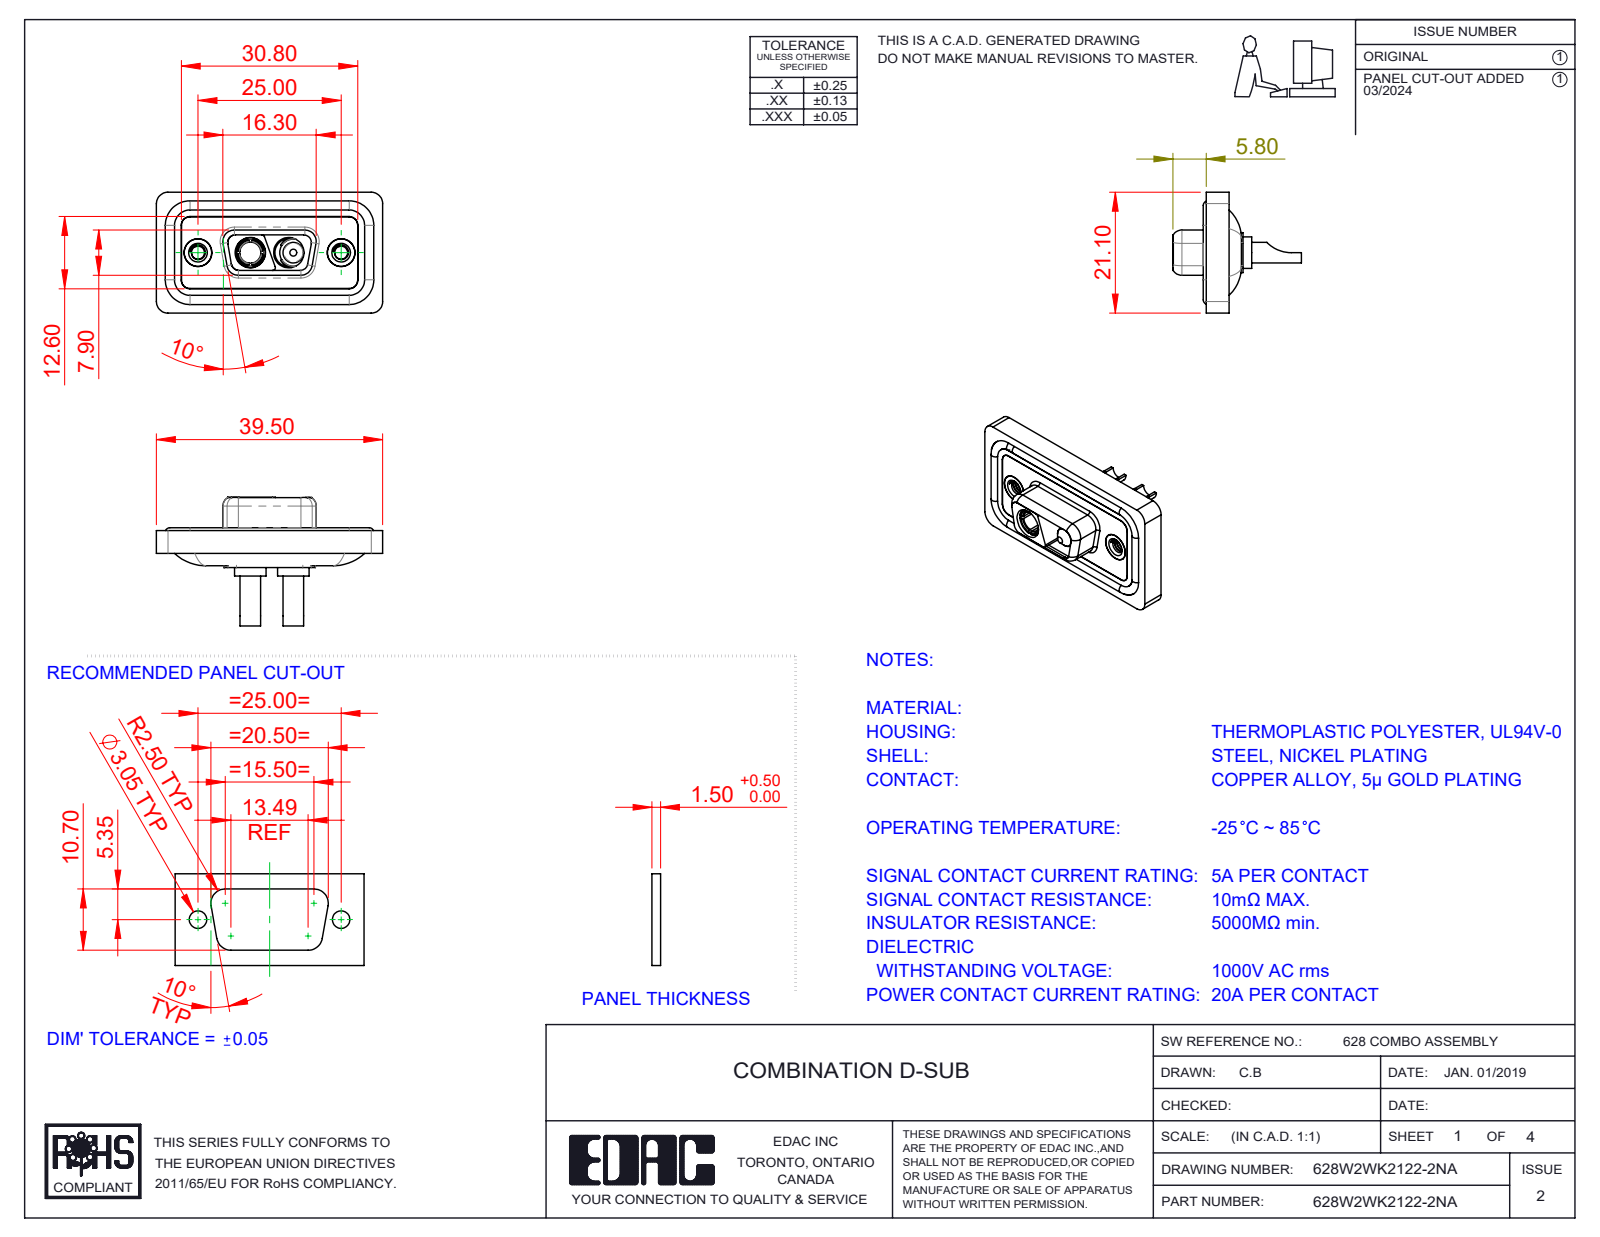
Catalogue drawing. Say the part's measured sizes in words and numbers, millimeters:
The part is named "628Combo Waterproof Housing_09 Contacts; 628Combo Shell Front_09 Contacts; 628Combo Shell Rear_09 Contacts; 628Combo Threaded Rivet_A (+4 more)". Its 3-D file was written by "SolidWorks 2023 (CONFIG_CONTROL_DESIGN)". It is 11 solids with 510 faces: 150 planar, 239 cylindrical and 121 other. Overall it measures 39.5 by 22.45 by 21.1 millimeters. Its volume is 4 630 cubic millimeters and its surface area 7 506 square millimeters. Round holes: 4 of diameter 4.85, 2 of diameter 2.26, 2 of diameter 2.7, 2 of diameter 4, 2 of diameter 4.05, 2 of diameter 5, 2 of diameter 5.3, 1 of diameter 3.7. Round bosses or shafts: 4 of diameter 1.6, 2 of diameter 5.5, 2 of diameter 5.2, 2 of diameter 4.95, 2 of diameter 4.8, 2 of diameter 4.75, 2 of diameter 3.75, 2 of diameter 3.6. Partial cylindrical surfaces (rounded edges, fillets, slot ends): 22 of radius 1.5, 18 of radius 2, 8 of radius 1.35, 8 of radius 1.6, 6 of radius 0.5, 4 of radius 0.25, 4 of radius 0.6, 4 of radius 0.65. The main face-to-face distances are 0.4, 1.1, 2.9, 1.6, 0.5, 1.8, 5.65, 1.5, 5.35, 3.1. The hole center spacings are 9.14, 15.86, 6.72, 25.
